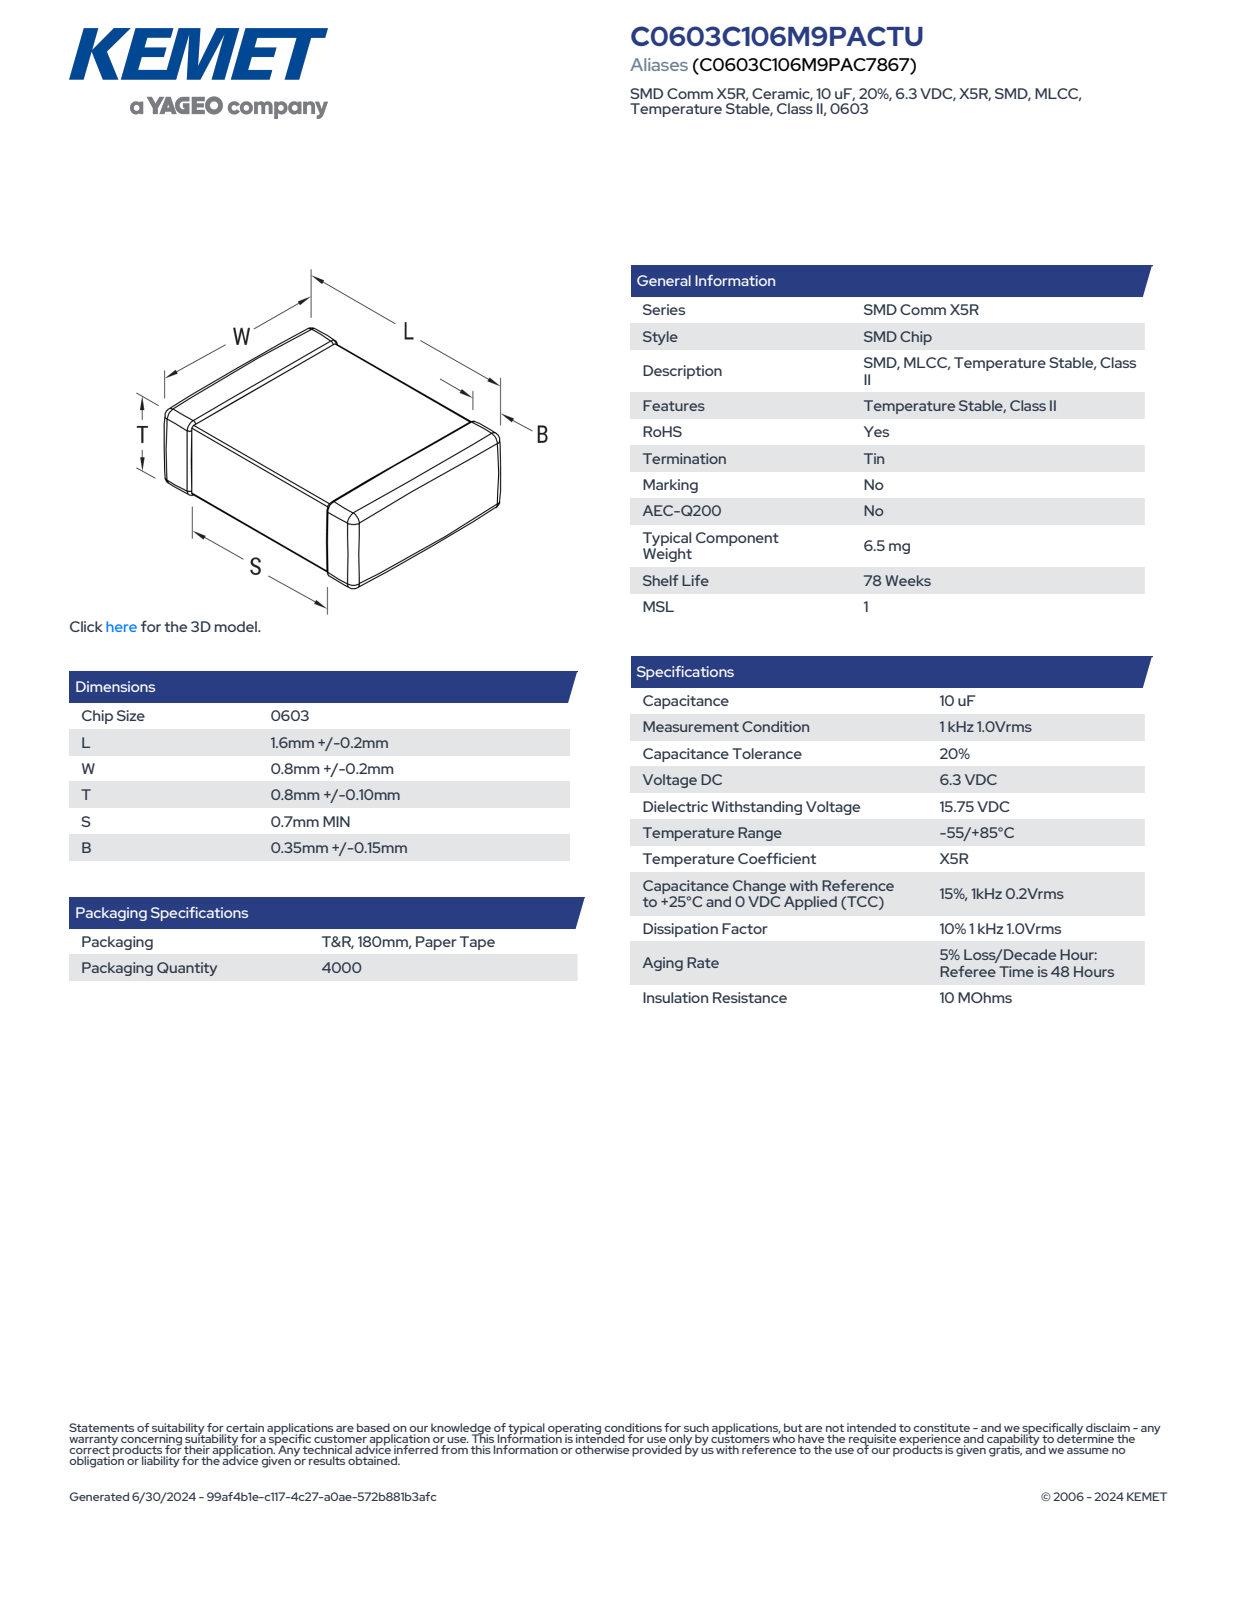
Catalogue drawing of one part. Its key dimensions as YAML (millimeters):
part_name: "CCS_CCSTD_0603_L1.8W1T0.9B0.35"
step_written_by: "SolidWorks 2014 (AUTOMOTIVE_DESIGN)"
units: millimeters
bodies: {solids: 4, faces: 125, planar: 71, cylindrical: 38, other: 16}
overall_size: [1.8, 1, 0.9]
volume: 2
surface_area: 9
face_to_face_distances: [0.88, 0.98, 0.86, 0.96, 1.8, 0.9, 1, 0.82, 0.97, 0.83]
